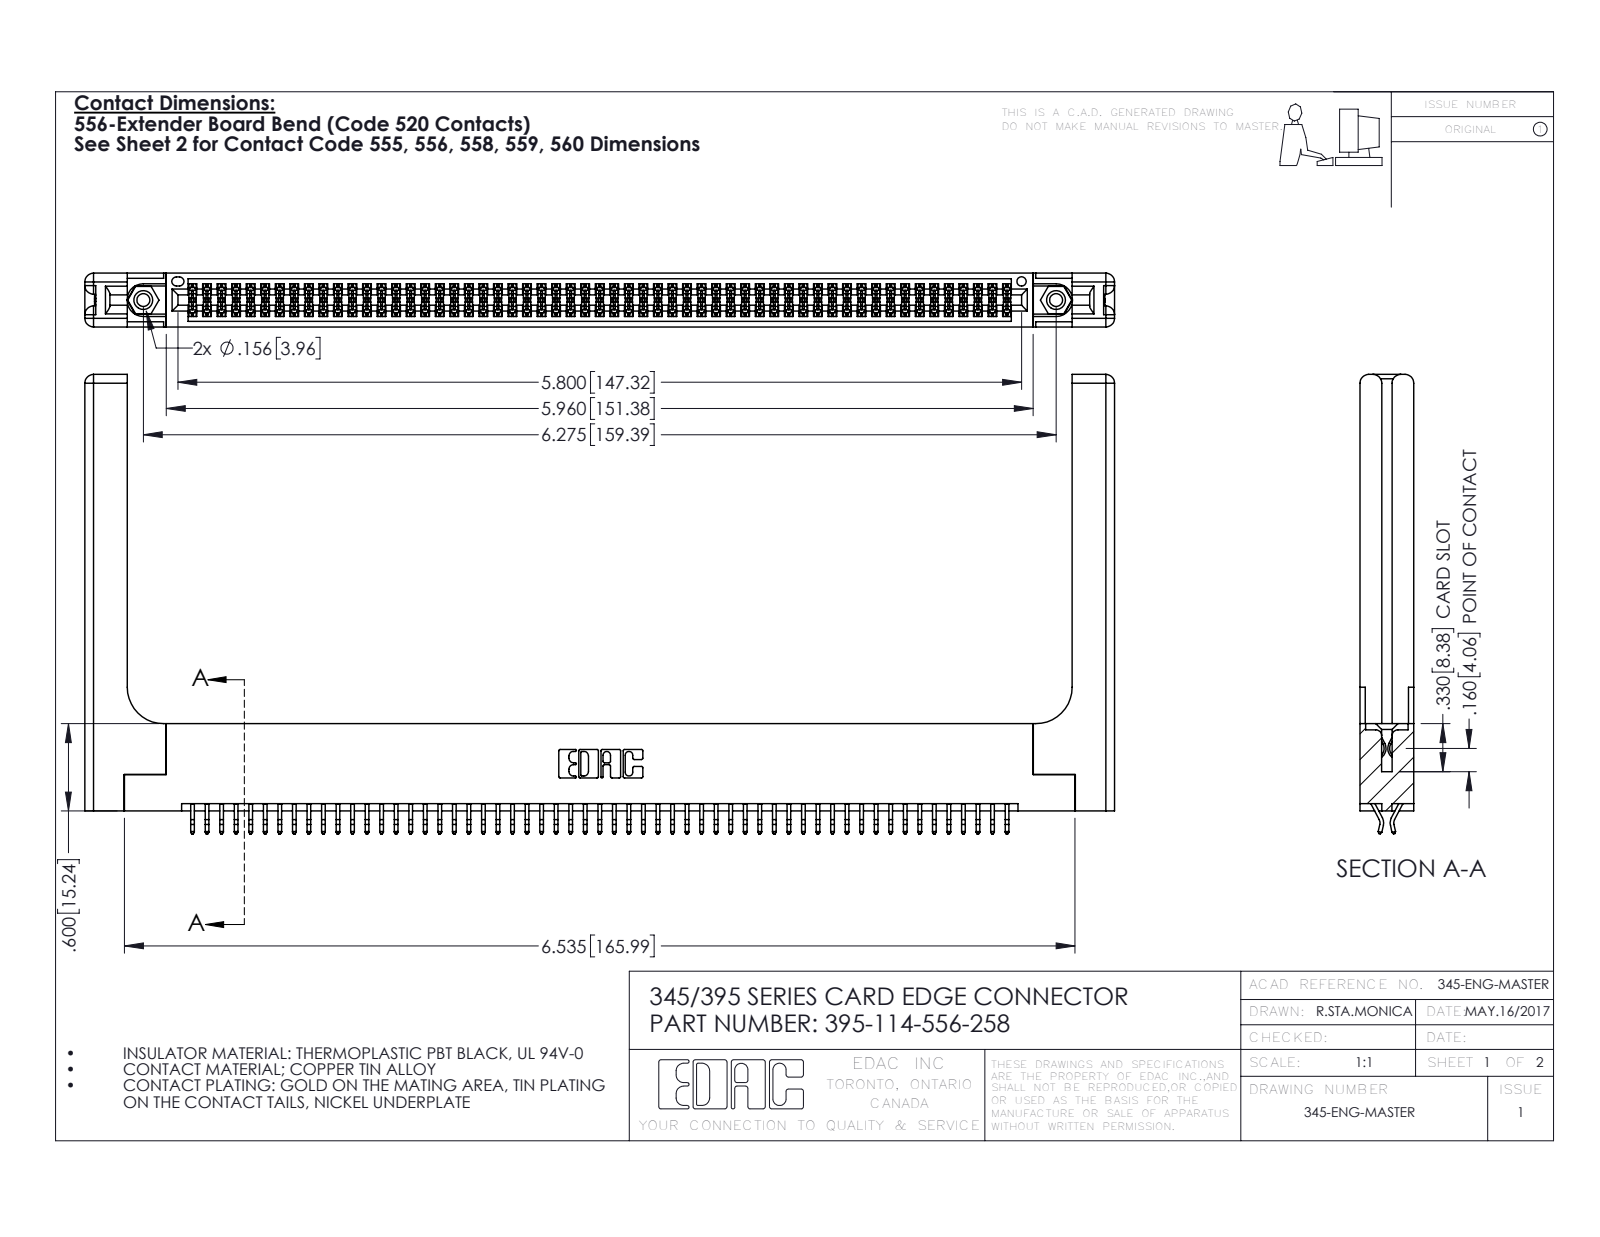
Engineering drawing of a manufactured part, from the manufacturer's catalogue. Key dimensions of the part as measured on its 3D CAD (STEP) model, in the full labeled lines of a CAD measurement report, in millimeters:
Part name (STEP PRODUCT): 345-292-001_556 Tail; 395-114-556-258; 345 Part_Flush Mounting Lugs - 0.156 Dia-TH; 345-220-058_345-220-058 (+1 more)
STEP written by: SolidWorks 2016 (CONFIG_CONTROL_DESIGN)
Units: millimetres
Bodies: 119 solids, 6766 faces (4446 planar, 2260 cylindrical, 60 other)
Overall size (bounding box): 179.8 × 80.2 × 9.4
Volume: 26 070 mm³ · Surface area: 31 260 mm²
Round holes (diameter × count): ⌀2.3 ×2, ⌀3.2 ×2, ⌀4 ×2, ⌀1.6 ×1
Round bosses / shafts (diameter × count): ⌀3.9 ×2
Partial cylindrical surfaces — rounded edges, fillets, slot ends (radius × count): R0.2 ×171, R0.3 ×22, R1.5 ×16, R0.2 ×6, R0.8 ×6, R0.7 ×3, R0.3 ×2, R0.4 ×2
Main face-to-face distances: 1.8, 7.6, 9.4, 5.1, 0.6, 2.5, 6.9, 5.7, 3.8, 3.8
Hole centre spacings: 6.9, 153.4, 159.4
